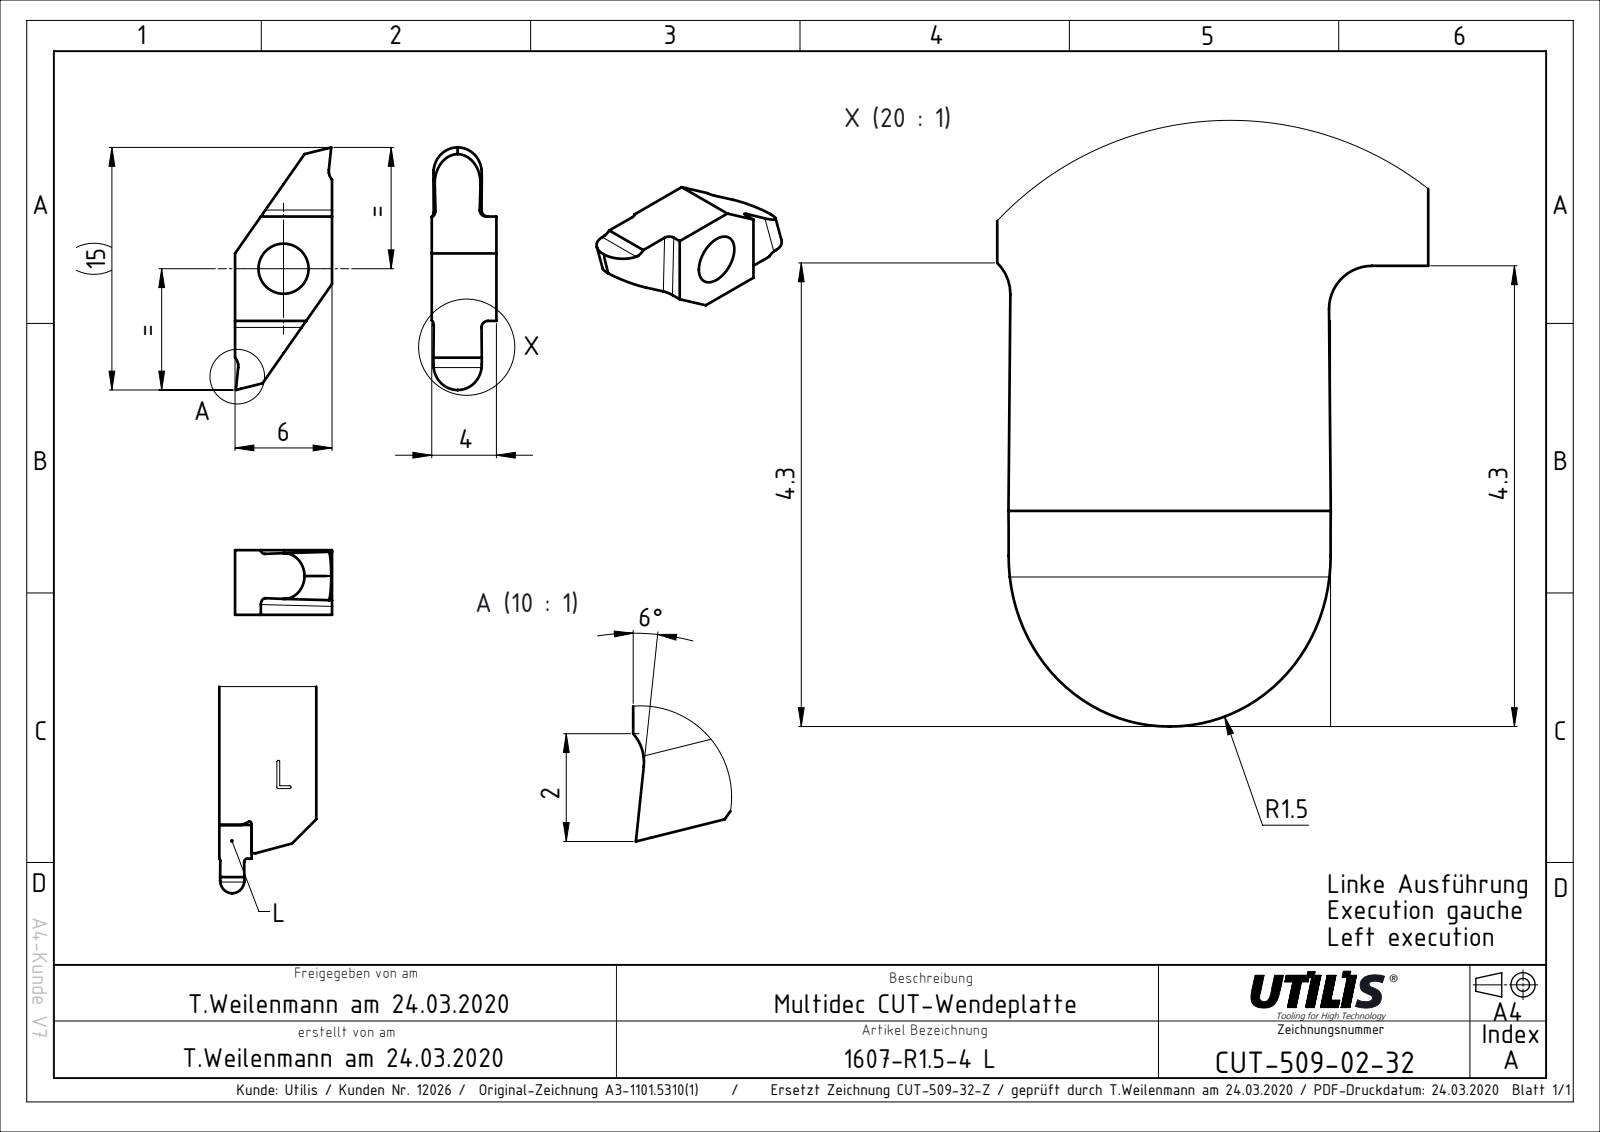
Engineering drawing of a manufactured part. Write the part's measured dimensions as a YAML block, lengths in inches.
part_name: "CUT-509-02; ASME Y14.5"
step_written_by: "FormatWorks Professional (AP242_MANAGED_MODEL_BASED_3D_ENGINEERING_MIM_LF)"
units: inches
bodies: {solids: 1, faces: 28, planar: 12, cylindrical: 14, other: 2}
overall_size: [0.591, 0.236, 0.157]
volume: 0.011
surface_area: 0.408
round_holes:
  - {diameter: 0.122, count: 1}
partial_cylinders:
  - {radius: 0.059, count: 4}
  - {radius: 0.016, count: 2}
face_to_face_distances: [0.236, 0.157, 0.107, 0.254]
